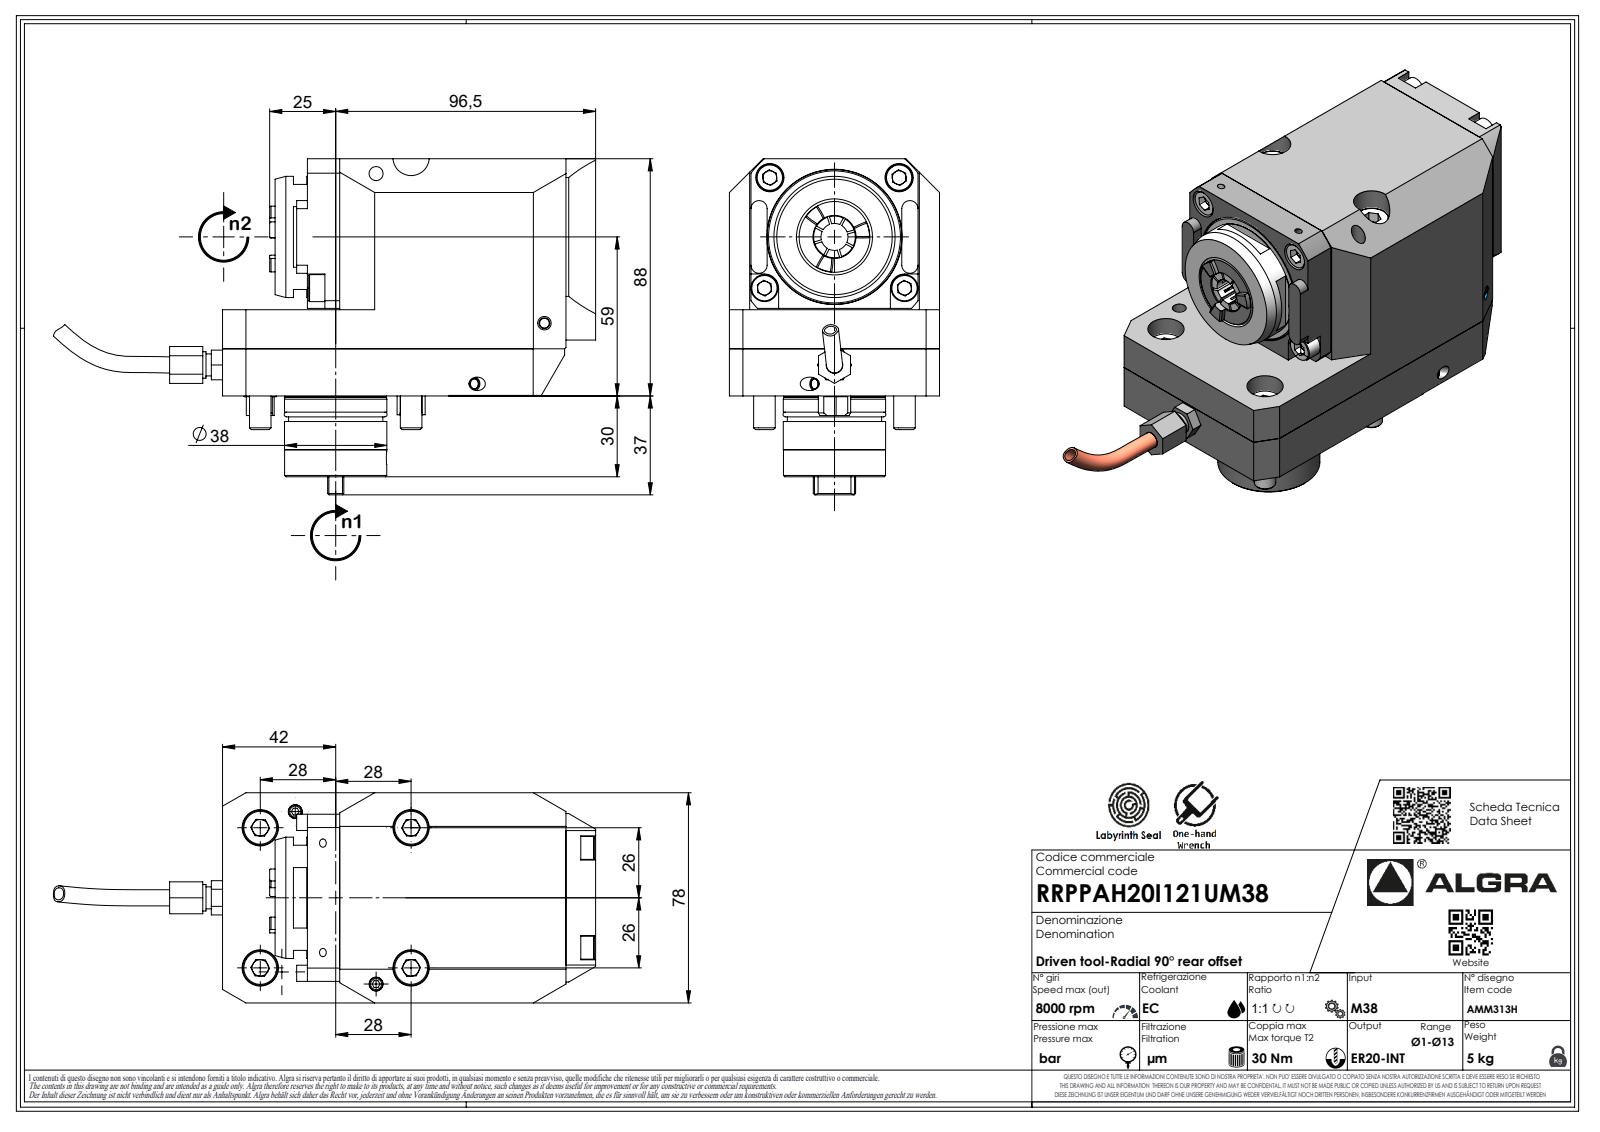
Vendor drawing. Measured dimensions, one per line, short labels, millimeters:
name: RRPPAH20I121UM38
written by: SolidWorks 2023 (AUTOMOTIVE_DESIGN)
unit: mm
bodies: 1 solid, 467 faces (317 planar, 51 cylindrical, 99 other)
size: 138.5 × 124.7 × 78
volume: 789 544 mm³; area: 59 434 mm²
holes: 1× ⌀2.1
bosses: 1× ⌀45, 1× ⌀38, 1× ⌀37.9, 1× ⌀37.6, 1× ⌀35, 1× ⌀12, 1× ⌀6.37, 1× ⌀1.7
rounds: 7× R0.33, 7× R0.52, 7× R3.7, 4× R3, 1× R0.21, 1× R6, 1× R7.85, 1× R25.1
face distances: 78, 88, 56, 32, 31.8, 87.8, 138.5, 19.5, 12, 62
